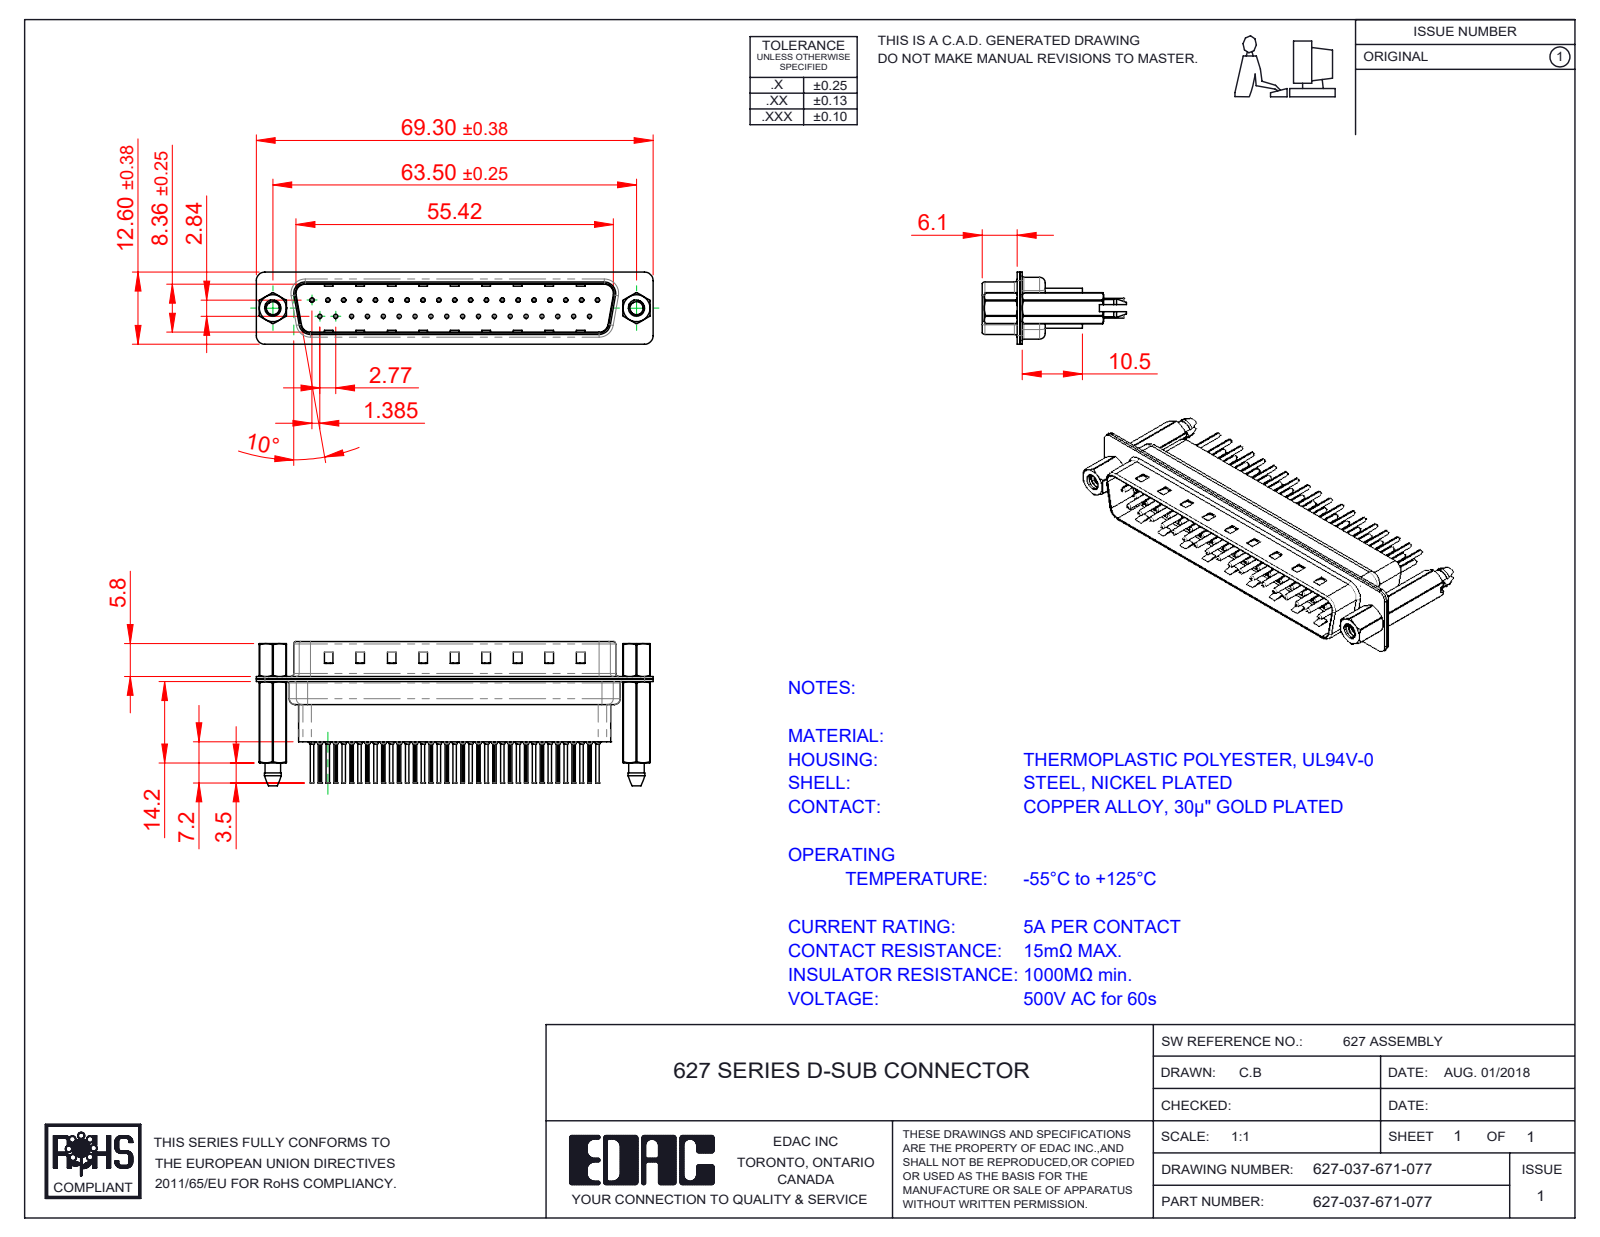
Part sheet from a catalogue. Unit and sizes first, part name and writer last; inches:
Units: inches
Overall size (bounding box): 2.728 × 0.988 × 0.496
Round holes (diameter × count): ⌀0.008 ×37, ⌀0.014 ×37, ⌀0.043 ×37, ⌀0.063 ×37, ⌀0.089 ×2, ⌀0.09 ×2, ⌀0.157 ×2, ⌀0.189 ×2
Round bosses / shafts (diameter × count): ⌀0.079 ×37, ⌀0.059 ×37, ⌀0.03 ×37, ⌀0.024 ×37, ⌀0.193 ×2, ⌀0.11 ×2
Partial cylindrical surfaces — rounded edges, fillets, slot ends (radius × count): R0.004 ×74, R0.059 ×18, R0.079 ×12, R0.063 ×10, R0.02 ×8, R0.01 ×4, R0.024 ×4, R0.026 ×4
Main face-to-face distances: 0.016, 0.032, 0.377, 0.018, 0.027, 0.302, 0.059, 0.043, 0.318, 0.345
Hole centre spacings: 0.124, 0.109, 0.218, 0.327, 0.198, 0.398, 0.436, 0.503
Volume: 0.361 in³ · Surface area: 23.54 in²
Bodies: 44 solids, 4272 faces (1145 planar, 1648 cylindrical, 1479 other)
Part name (STEP PRODUCT): 627 Contact Row 1_61; 627 4-40 Threaded Boardlock_HP71; 627 Contact Row 2_61; 627 4-40 Hex Standoff (+4 more)
STEP written by: SolidWorks 2020 (CONFIG_CONTROL_DESIGN)
